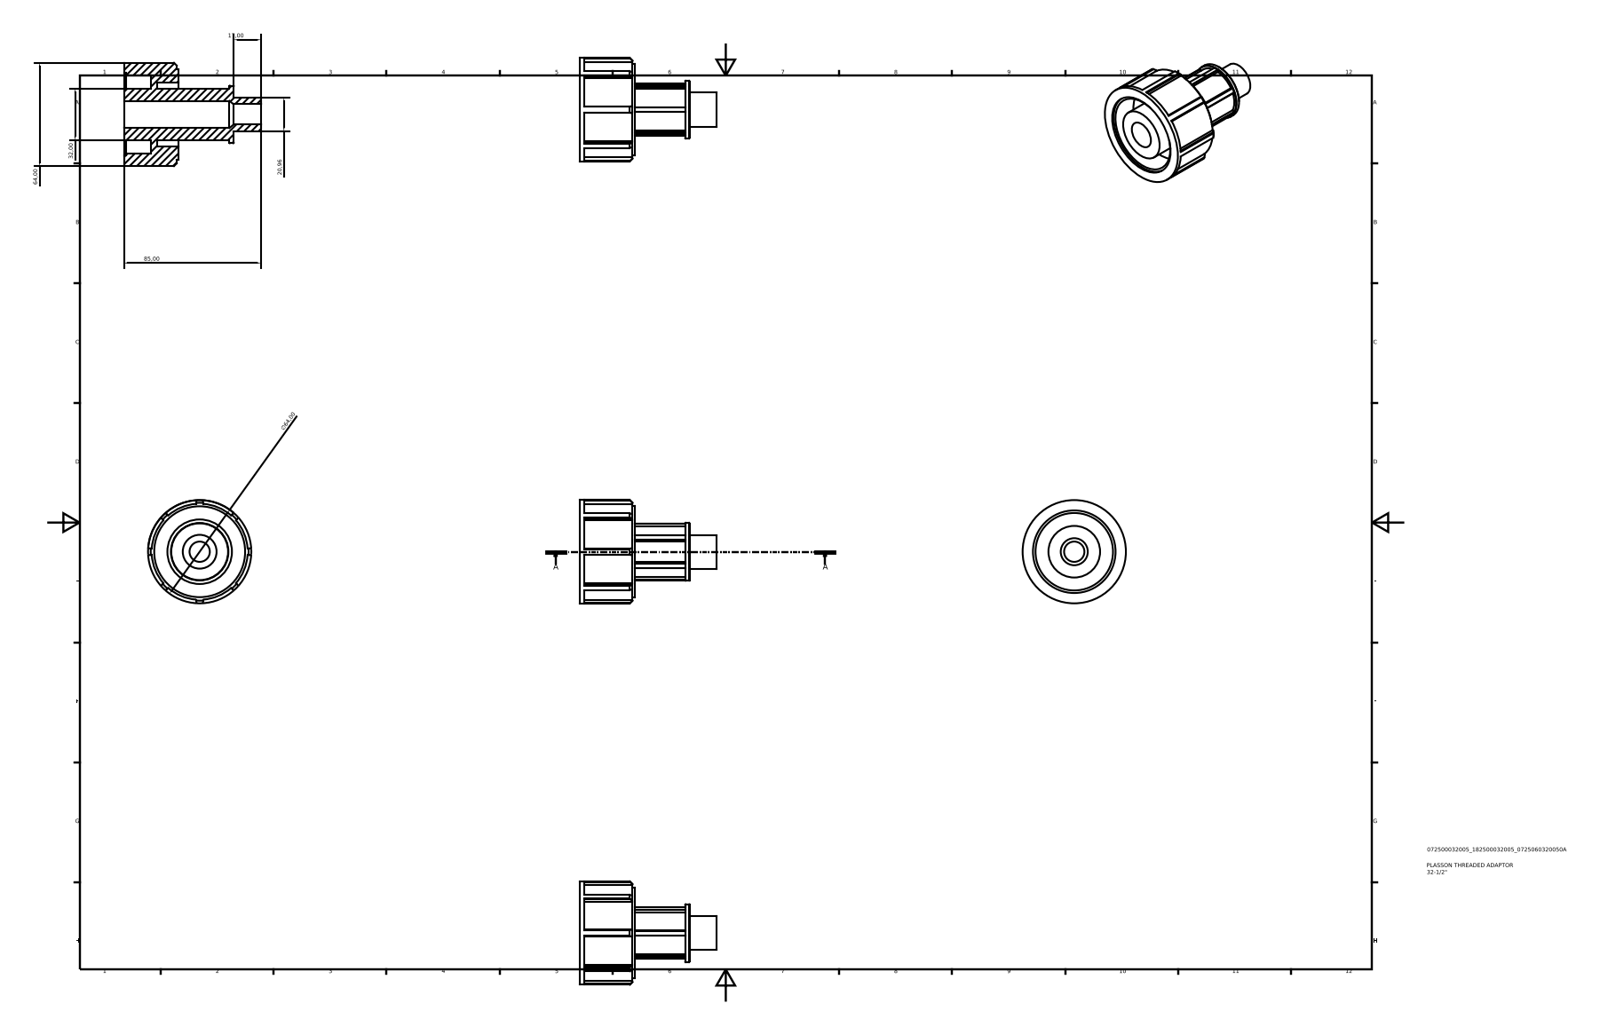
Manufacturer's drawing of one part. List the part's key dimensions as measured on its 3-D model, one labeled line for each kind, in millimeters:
Part name (STEP PRODUCT): 072500032005_182500032005
STEP written by: Autodesk Inventor 2015 (AUTOMOTIVE_DESIGN)
Units: millimetres
Bodies: 1 solid, 115 faces (74 planar, 30 cylindrical, 11 other)
Overall size (bounding box): 85 × 64 × 64
Volume: 92 035 mm³ · Surface area: 30 698 mm²
Round holes (diameter × count): ⌀12.57 ×1, ⌀16.76 ×1, ⌀40 ×1, ⌀48 ×1, ⌀51.2 ×1
Round bosses / shafts (diameter × count): ⌀64 ×1, ⌀59.52 ×1, ⌀56.32 ×1, ⌀35.62 ×1, ⌀32 ×1, ⌀20.95 ×1
Partial cylindrical surfaces — rounded edges, fillets, slot ends (radius × count): R17.6 ×1
Main face-to-face distances: 17, 34, 68, 51, 1.27, 32.73, 15.73, 2.55, 65.45, 31.45
